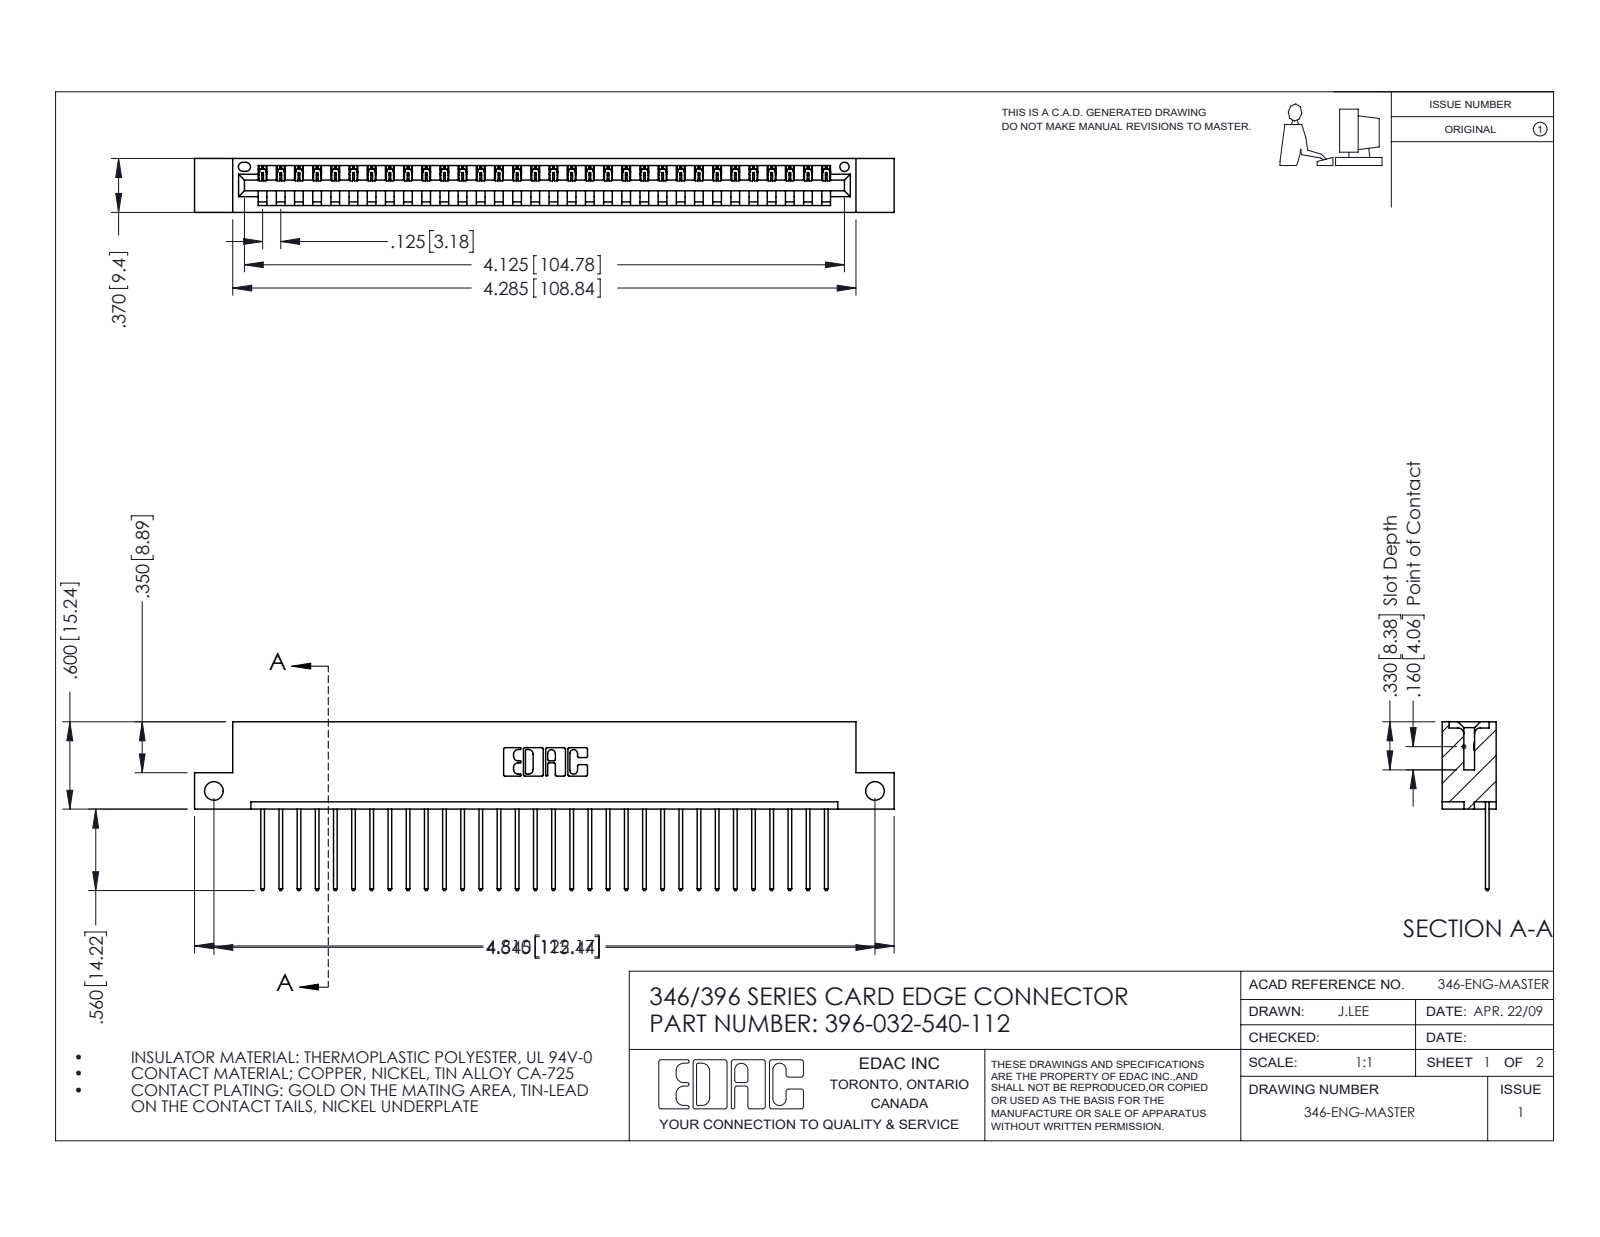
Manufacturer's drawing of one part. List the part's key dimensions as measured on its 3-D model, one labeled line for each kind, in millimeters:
Part name (STEP PRODUCT): 345-292-001_345-293-140; 396-032-540-112; 346 Part_Flush Mounting Lugs - Side Mount
STEP written by: SolidWorks 2016 (CONFIG_CONTROL_DESIGN)
Units: millimetres
Bodies: 33 solids, 1978 faces (1356 planar, 622 cylindrical, 0 other)
Overall size (bounding box): 122.2 × 29.5 × 9.4
Volume: 11 600 mm³ · Surface area: 14 540 mm²
Round holes (diameter × count): ⌀3.3 ×2, ⌀1.6 ×1
Partial cylindrical surfaces — rounded edges, fillets, slot ends (radius × count): R0.2 ×64, R0.3 ×64, R0.3 ×22, R0.2 ×6, R0.8 ×6, R0.7 ×3, R0.8 ×2, R1 ×2
Main face-to-face distances: 1.2, 8.2, 6.4, 9.4, 1.8, 7.6, 0.6, 3.8, 5.6, 2.5
Hole centre spacings: 115.4
